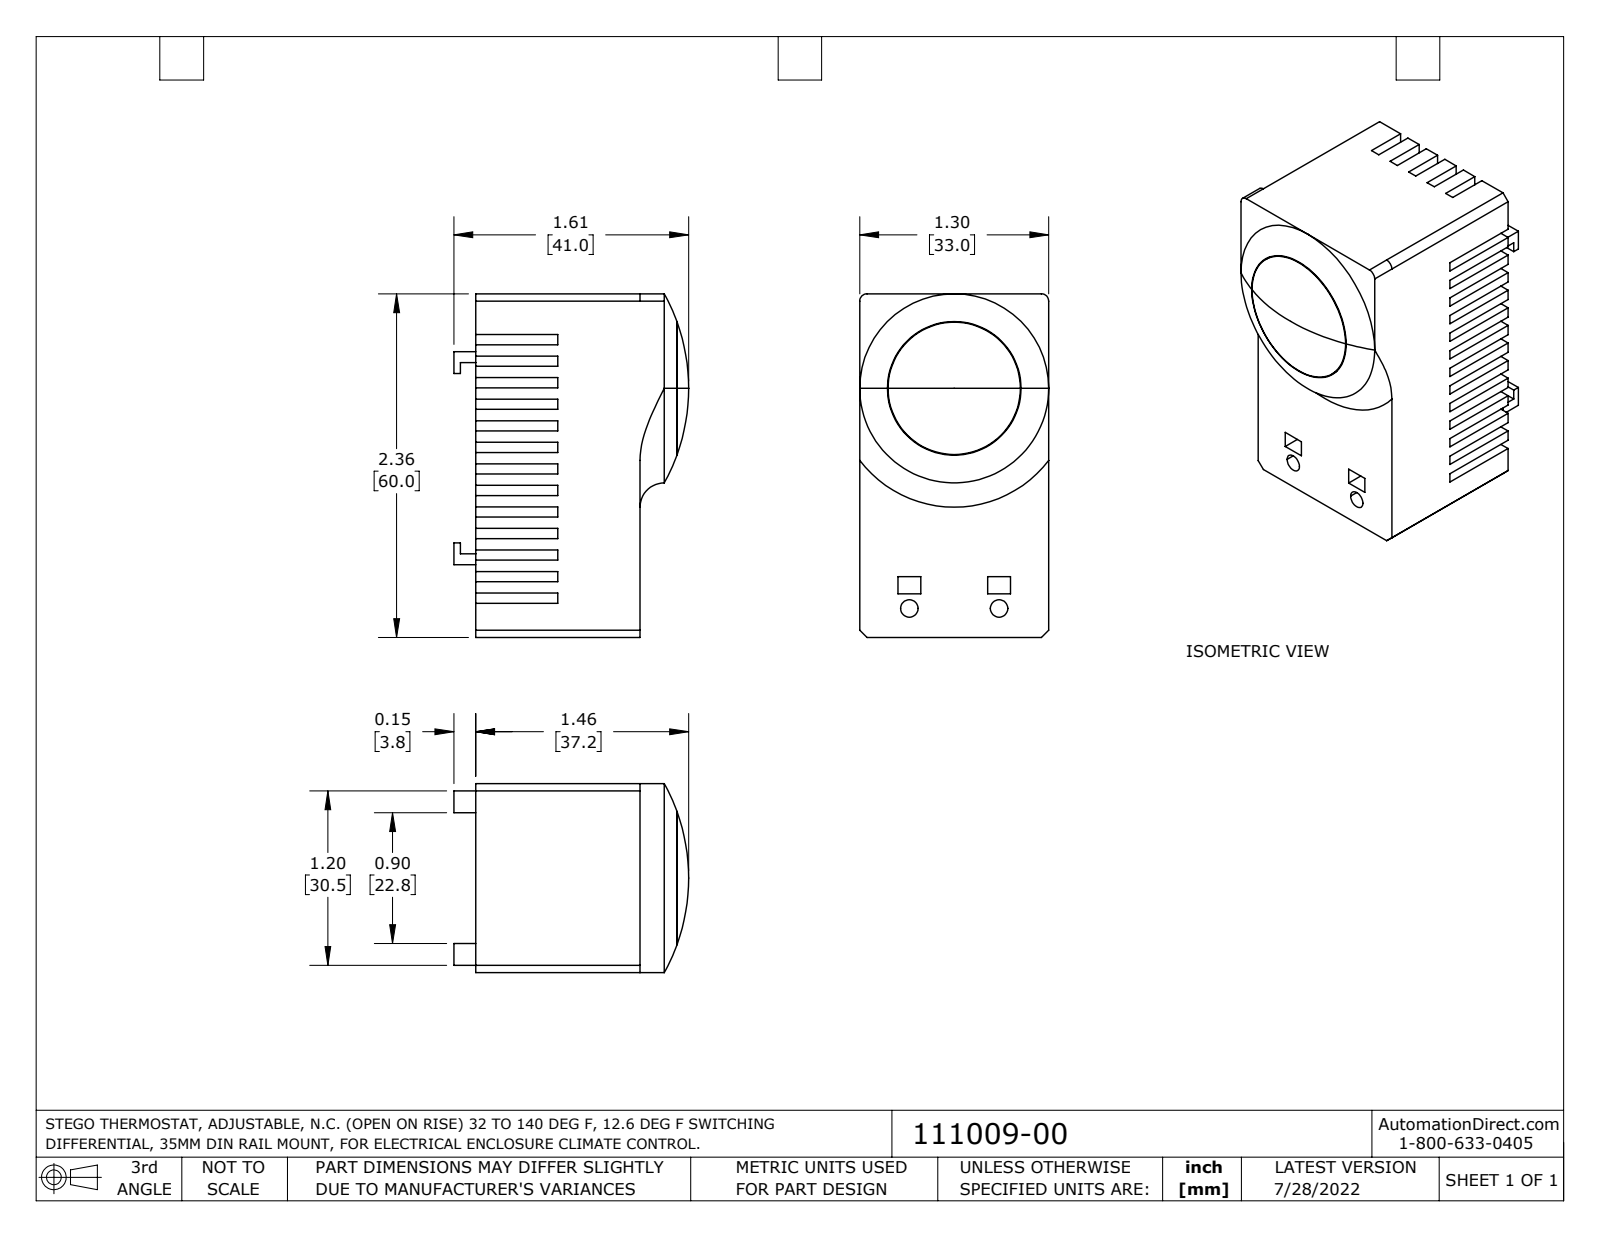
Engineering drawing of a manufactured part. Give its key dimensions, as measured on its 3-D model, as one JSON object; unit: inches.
{"part_name": "111009-00_Default", "step_written_by": "SolidWorks 2021 (CONFIG_CONTROL_DESIGN)", "units": "inches", "bodies": {"solids": 1, "faces": 198, "planar": 183, "cylindrical": 10, "other": 5}, "overall_size": [2.362, 1.614, 1.299], "volume_in3": 3.737, "surface_area_in2": 19.92, "round_holes": [[0.12, 2], [0.919, 1]], "round_bosses_or_shafts": [[0.909, 1]], "partial_cylinders_radius": [[0.05, 2]], "face_to_face_distances": [1.299, 0.148, 0.07, 2.362, 0.296, 1.13, 0.444, 0.592, 0.078, 0.218], "hole_center_spacings": [1.544, 0.617]}
